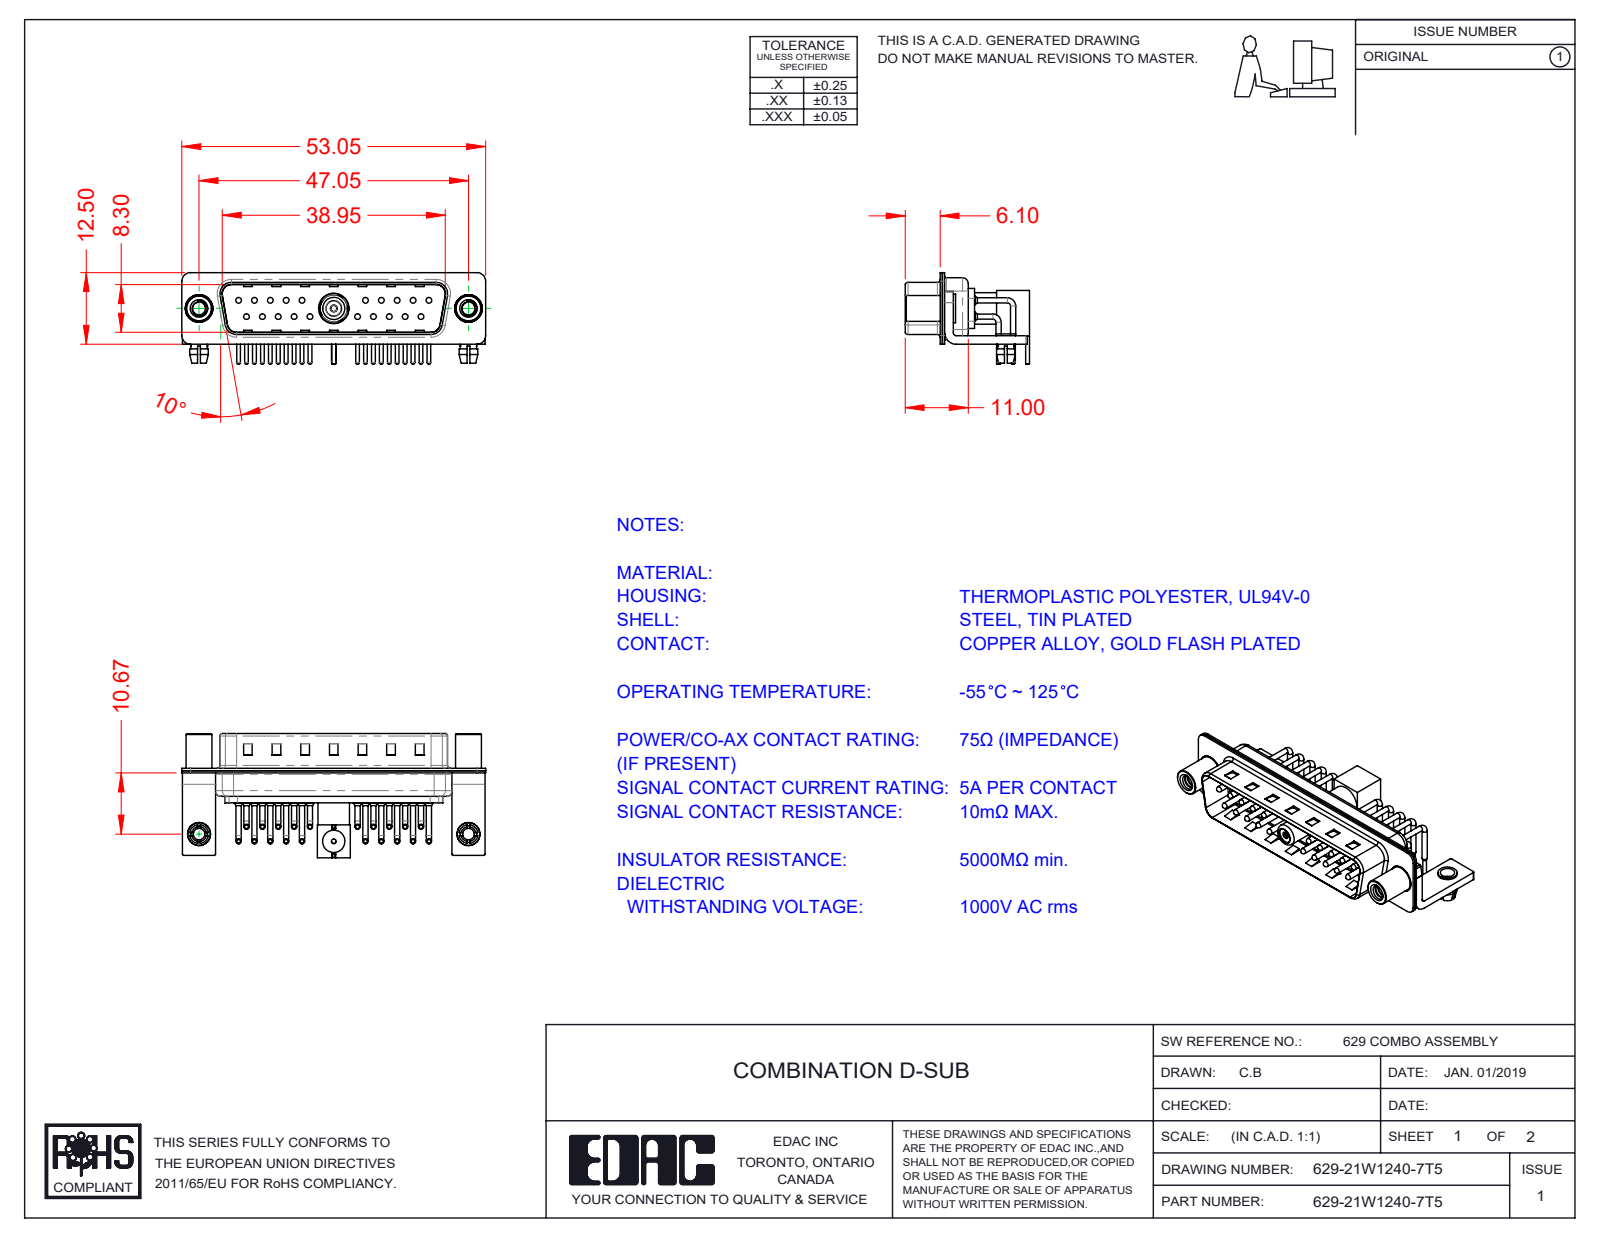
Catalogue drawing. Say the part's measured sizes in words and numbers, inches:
The part is named "629Combo Shell Rear_25 Contacts; 629Combo Contact Row 2; Co-Ax Jack Assy_RA; Socket_RA (+8 more)". Its 3-D file was written by "SolidWorks 2020 (CONFIG_CONTROL_DESIGN)". It is 36 solids with 2908 faces: 1578 planar, 1016 cylindrical and 314 other. Overall it measures 2.089 by 0.855 by 0.63 inches. Its volume is 0.22 cubic inches and its surface area 14.83 square inches. Round holes: 22 of diameter 0.079, 21 of diameter 0.063, 20 of diameter 0.03, 3 of diameter 0.098, 2 of diameter 0.089, 2 of diameter 0.126, 2 of diameter 0.157, 2 of diameter 0.189, 1 of diameter 0.031, 1 of diameter 0.043, 1 of diameter 0.047, 1 of diameter 0.059. Round bosses or shafts: 40 of diameter 0.035, 20 of diameter 0.059, 20 of diameter 0.039, 20 of diameter 0.026, 3 of diameter 0.157, 3 of diameter 0.13, 3 of diameter 0.114, 2 of diameter 0.197. Partial cylindrical surfaces (rounded edges, fillets, slot ends): 20 of radius 0.04, 16 of radius 0.01, 16 of radius 0.059, 13 of radius 0.079, 9 of radius 0.02, 8 of radius 0.063, 4 of radius 0.024, 4 of radius 0.026. The main face-to-face distances are 0.016, 0.031, 0.374, 0.358, 0.343, 0.059, 0.39, 0.024, 0.014, 0.083. The hole center spacings are 0.124, 0.109, 0.218, 0.327, 0.198, 0.763, 0.826, 0.872.
